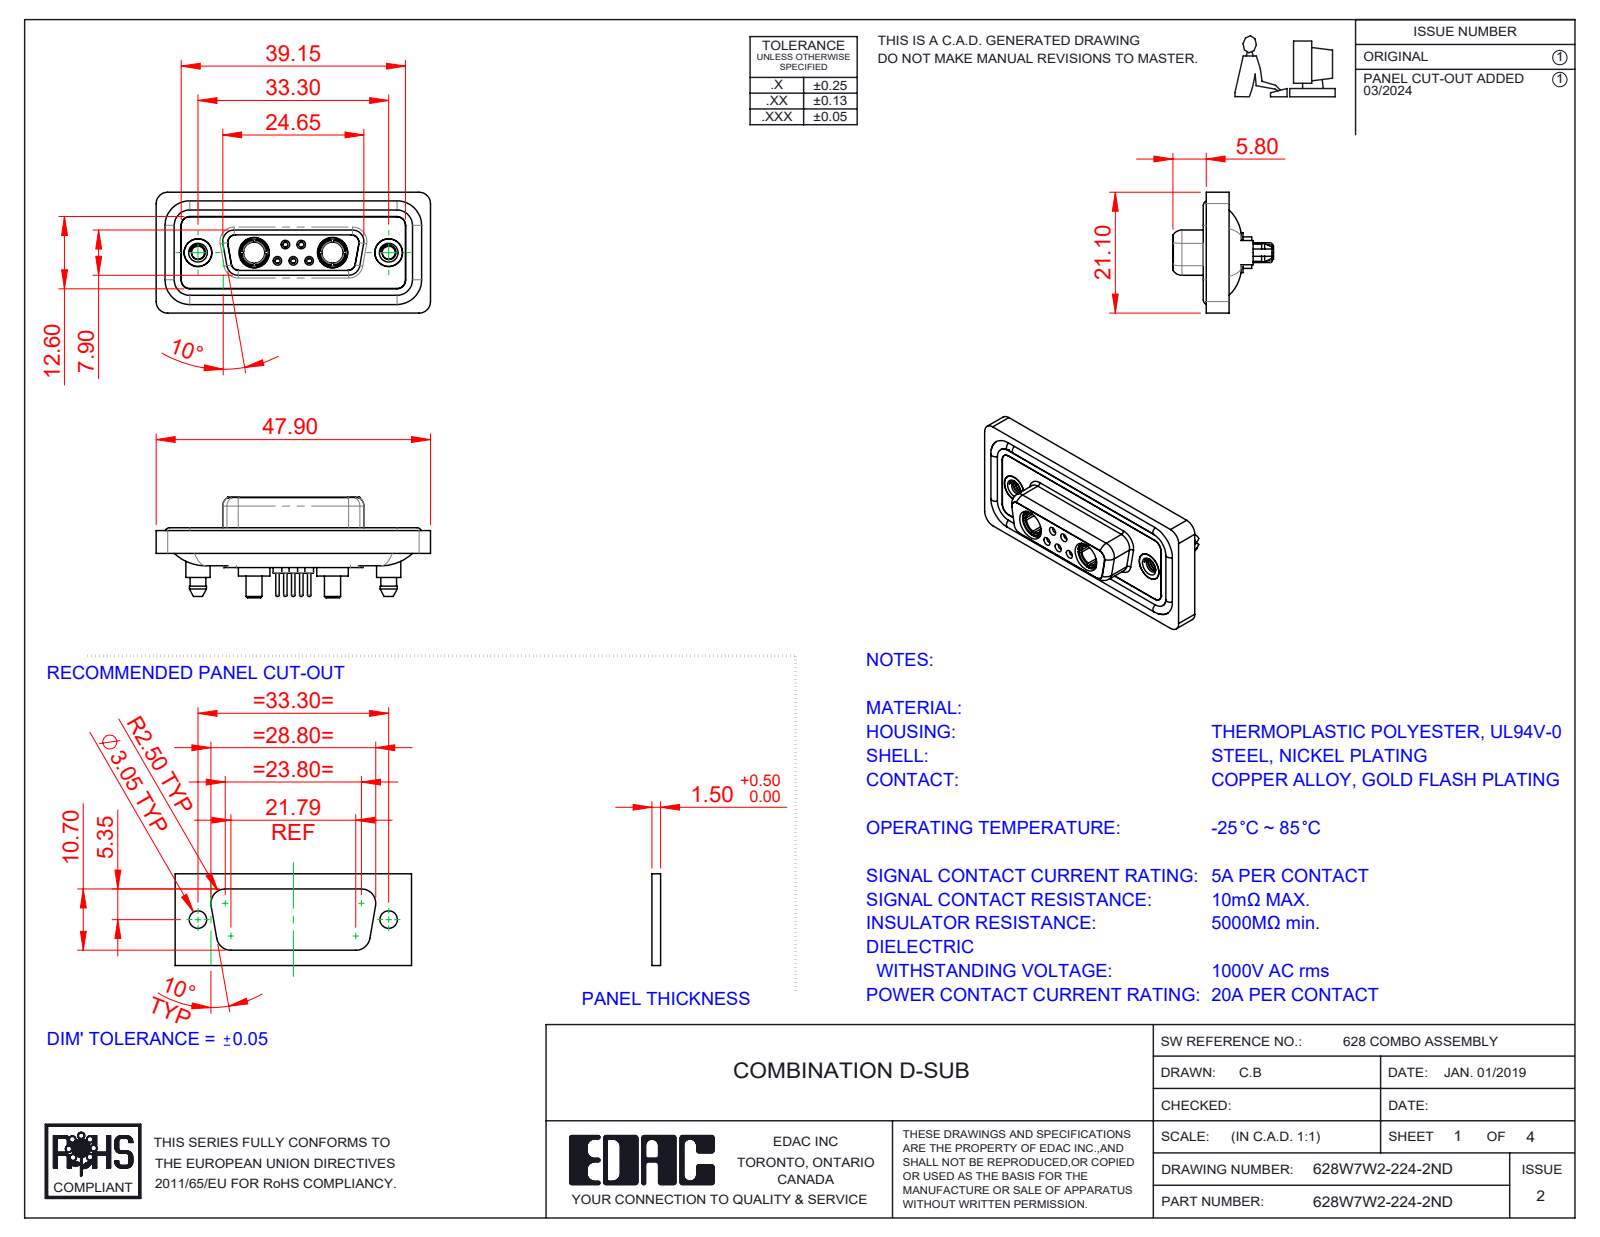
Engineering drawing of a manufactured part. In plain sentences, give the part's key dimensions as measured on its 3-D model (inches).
The part is named "628Combo Contact Row 1_24; 628Combo Housing_7W2; 628Combo Threaded Boardlock_D; 628Combo Contact Row 2_24 (+5 more)". Its 3-D file was written by "SolidWorks 2023 (CONFIG_CONTROL_DESIGN)". It is 16 solids with 875 faces: 254 planar, 377 cylindrical and 244 other. Overall it measures 1.886 by 0.831 by 0.691 inches. Its volume is 0.379 cubic inches and its surface area 15.85 square inches. Round holes: 5 of diameter 0.035, 5 of diameter 0.043, 5 of diameter 0.059, 5 of diameter 0.079, 4 of diameter 0.191, 3 of diameter 0.063, 2 of diameter 0.067, 2 of diameter 0.089, 2 of diameter 0.146, 2 of diameter 0.157, 2 of diameter 0.159, 2 of diameter 0.197. Round bosses or shafts: 6 of diameter 0.063, 5 of diameter 0.087, 5 of diameter 0.024, 2 of diameter 0.217, 2 of diameter 0.213, 2 of diameter 0.205, 2 of diameter 0.195, 2 of diameter 0.195. Partial cylindrical surfaces (rounded edges, fillets, slot ends): 24 of radius 0.059, 20 of radius 0.079, 12 of radius 0.053, 10 of radius 0.063, 4 of radius 0.01, 4 of radius 0.02, 4 of radius 0.024, 4 of radius 0.026. The main face-to-face distances are 0.016, 0.071, 0.063, 0.02, 0.114, 0.043, 0.293, 0.222, 0.26, 0.278. The hole center spacings are 0.124, 0.109, 0.386, 0.925, 0.17, 0.17, 0.198, 0.198.
